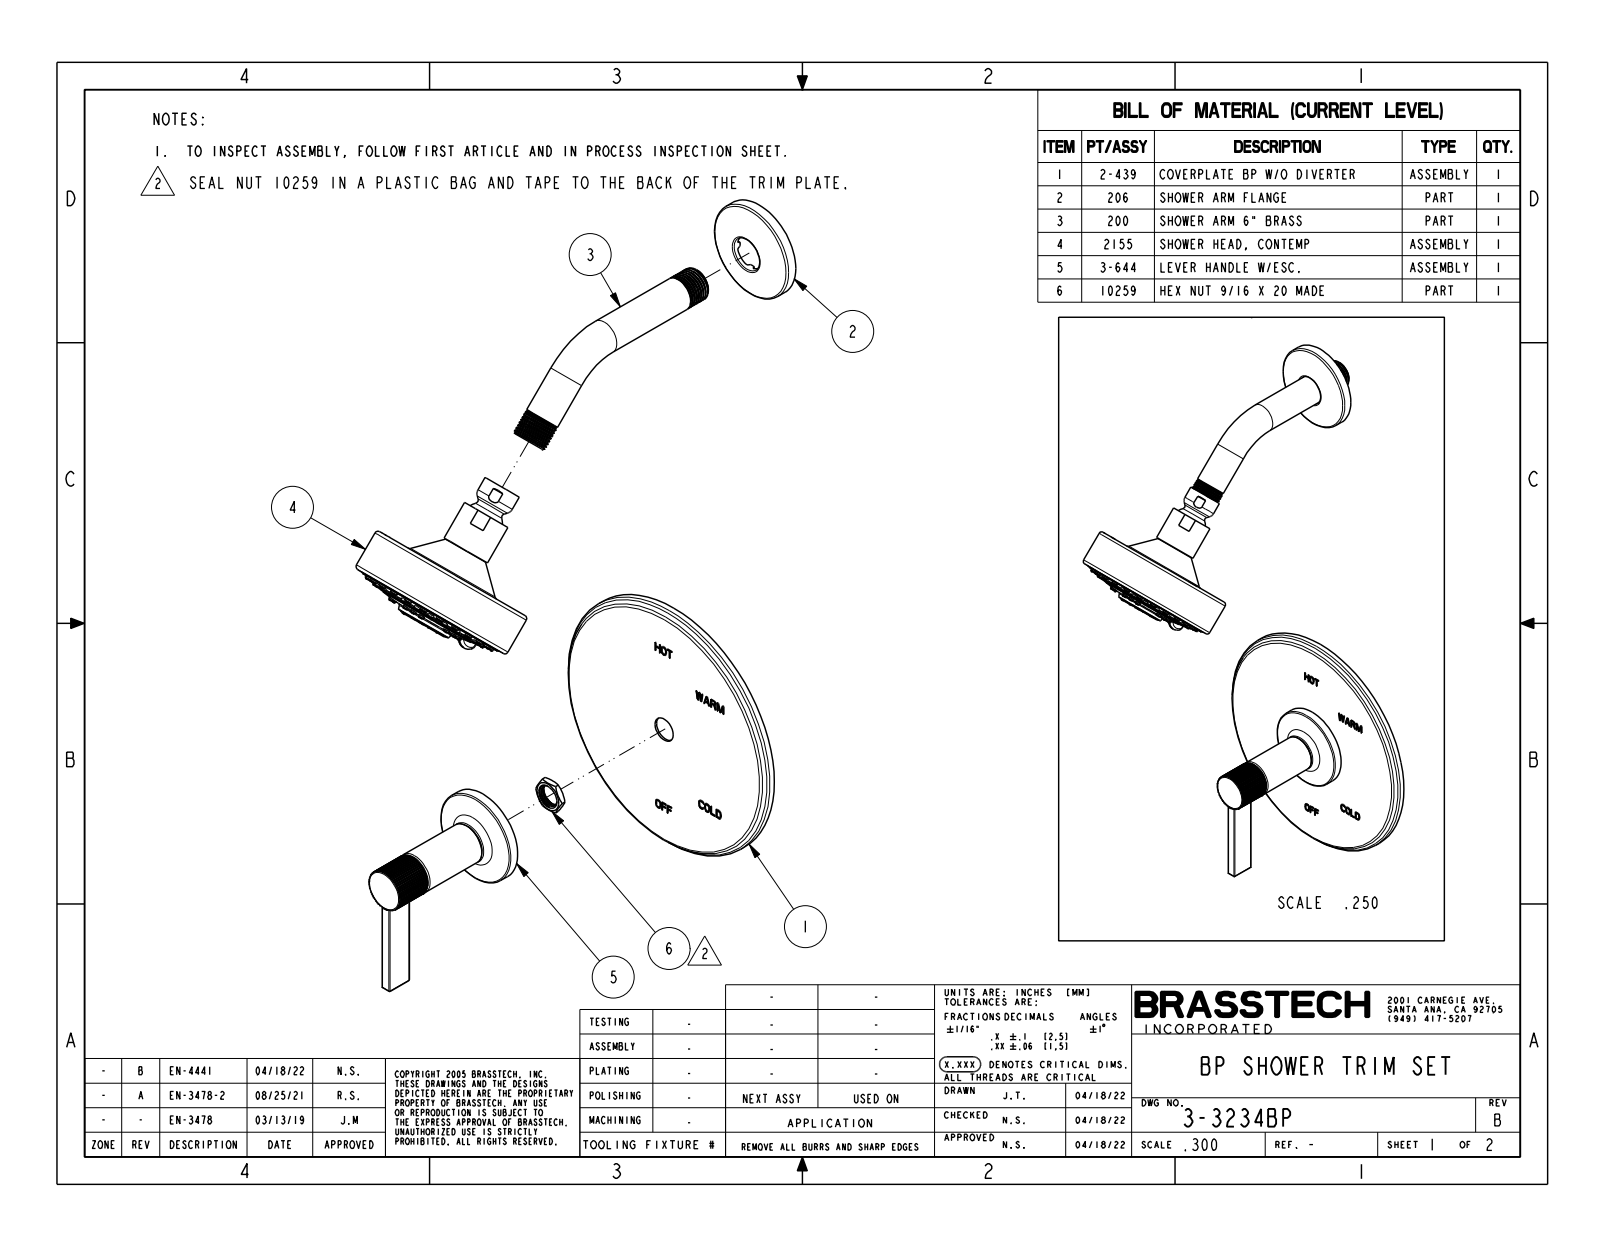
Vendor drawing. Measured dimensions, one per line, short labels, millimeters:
name: 11117; H-78; 2-439_ASM; 206 (+8 more)
written by: CREO PARAMETRIC BY PTC INC, 2018400 (CONFIG_CONTROL_DESIGN)
unit: mm
bodies: 54 solids, 8131 faces (3771 planar, 2002 cylindrical, 2358 other)
size: 417.6 × 227.2 × 165.1
volume: 249 600 mm³; area: 381 700 mm²
holes: 32× ⌀1.1, 15× ⌀2.5, 12× ⌀1.5, 8× ⌀2, 8× ⌀2.4, 8× ⌀4.7, 7× ⌀3, 3× ⌀3.8, 3× ⌀6.4, 3× ⌀7, 2× ⌀2.8, 2× ⌀6.8
bosses: 39× ⌀3.6, 23× ⌀4.2, 3× ⌀8, 3× ⌀6.2, 2× ⌀25.4, 2× ⌀20.7, 2× ⌀19.5, 2× ⌀5.8
rounds: 52× R0.5, 29× R0.3, 15× R2.1, 14× R0.2, 12× R0.5, 12× R0.8, 9× R2, 8× R2.2
face distances: 1.3, 2.5, 5.3, 17.7, 1, 16.7, 11.4, 12.4, 7.8, 19.2
hole spacings: 9.6, 10.7, 7, 5.3, 7, 9.4, 10.7, 15.4
